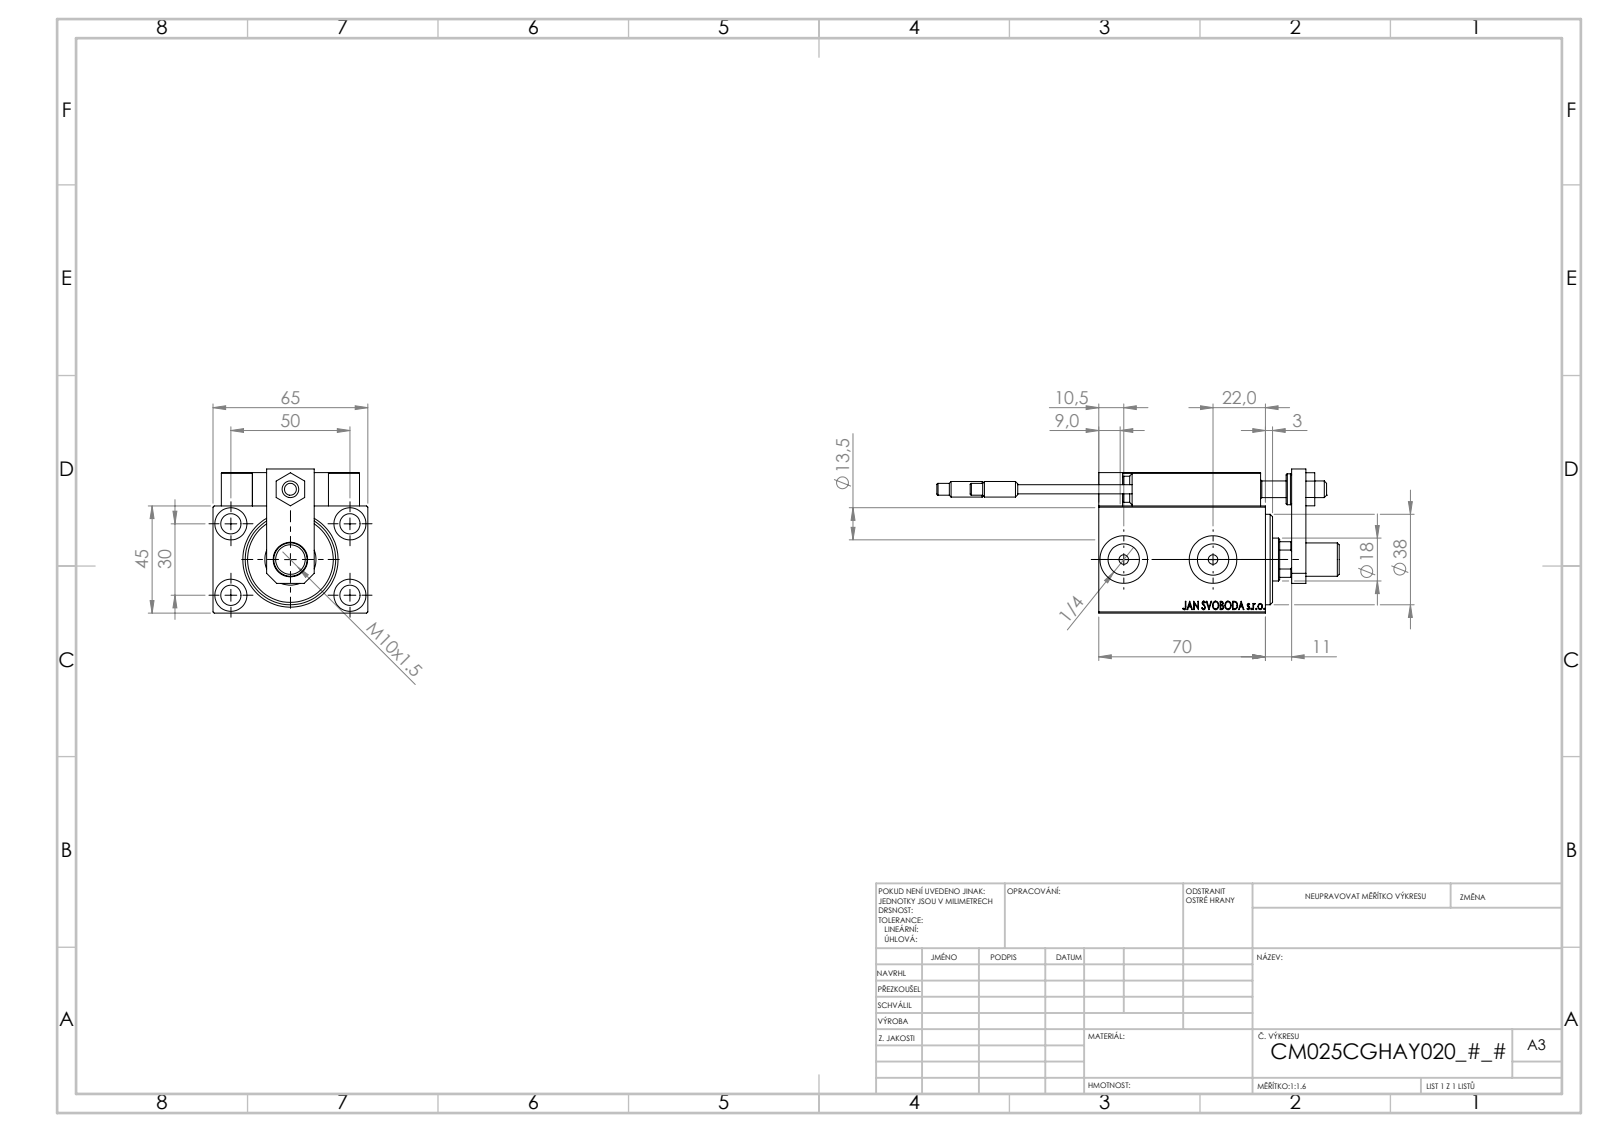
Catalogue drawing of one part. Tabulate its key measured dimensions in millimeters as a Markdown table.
| quantity | value |
| --- | --- |
| part name | V450CM_C_Body; SWITCH X; SWITCH_X_FRONT_BACK; Block (+7 more) |
| STEP written by | SolidWorks 2019 (CONFIG_CONTROL_DESIGN) |
| units | millimeters |
| bodies | 24 solids, 1317 faces (565 planar, 200 cylindrical, 552 other) |
| overall size | 169 × 65 × 60.5 |
| volume | 227 247 mm³ |
| surface area | 72 734 mm² |
| round holes (diameter × count) | 4 × 6, 8 × 5, 8.5 × 5, 3.2 × 4, 13.5 × 4, 5 × 2, 13.16 × 2, 20 × 2, 7 × 1, 14.5 × 1, 18 × 1, 21.5 × 1 |
| round bosses / shafts (diameter × count) | 5 × 4, 6.5 × 2, 3.8 × 2, 14 × 1, 13 × 1, 12 × 1, 11 × 1 |
| partial cylindrical surfaces (radius × count) | 0.3 × 30, 3 × 2, 8.5 × 1 |
| main face-to-face distances | 45, 59, 65, 14, 6, 3, 7, 20, 13, 3.5 |
| hole center spacings | 29.15, 11.37, 20, 22.09, 28.9, 29.59, 29.69, 30 |
